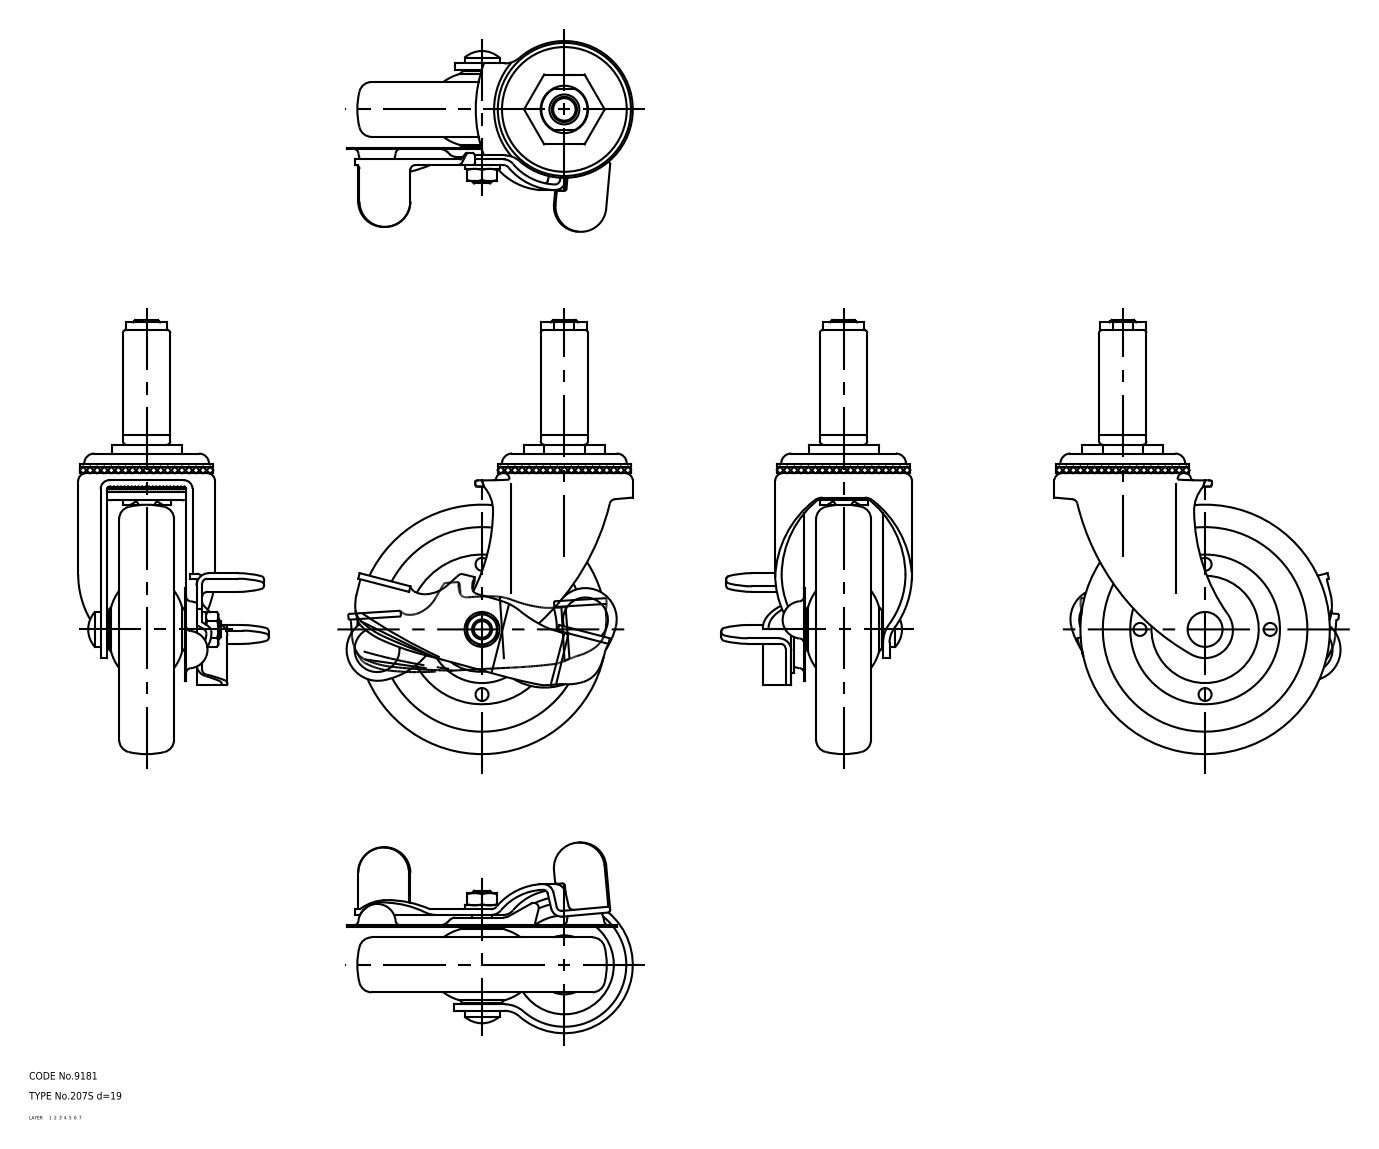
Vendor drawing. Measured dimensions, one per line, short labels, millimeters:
name: wheel; plate; main shaft; lever (+2 more)
written by: CADfix (AUTOMOTIVE_DESIGN)
unit: mm
bodies: 6 solids, 378 faces (0 planar, 0 cylindrical, 378 other)
size: 174 × 114.71 × 76.55
volume: 207 729 mm³; area: 68 127 mm²
